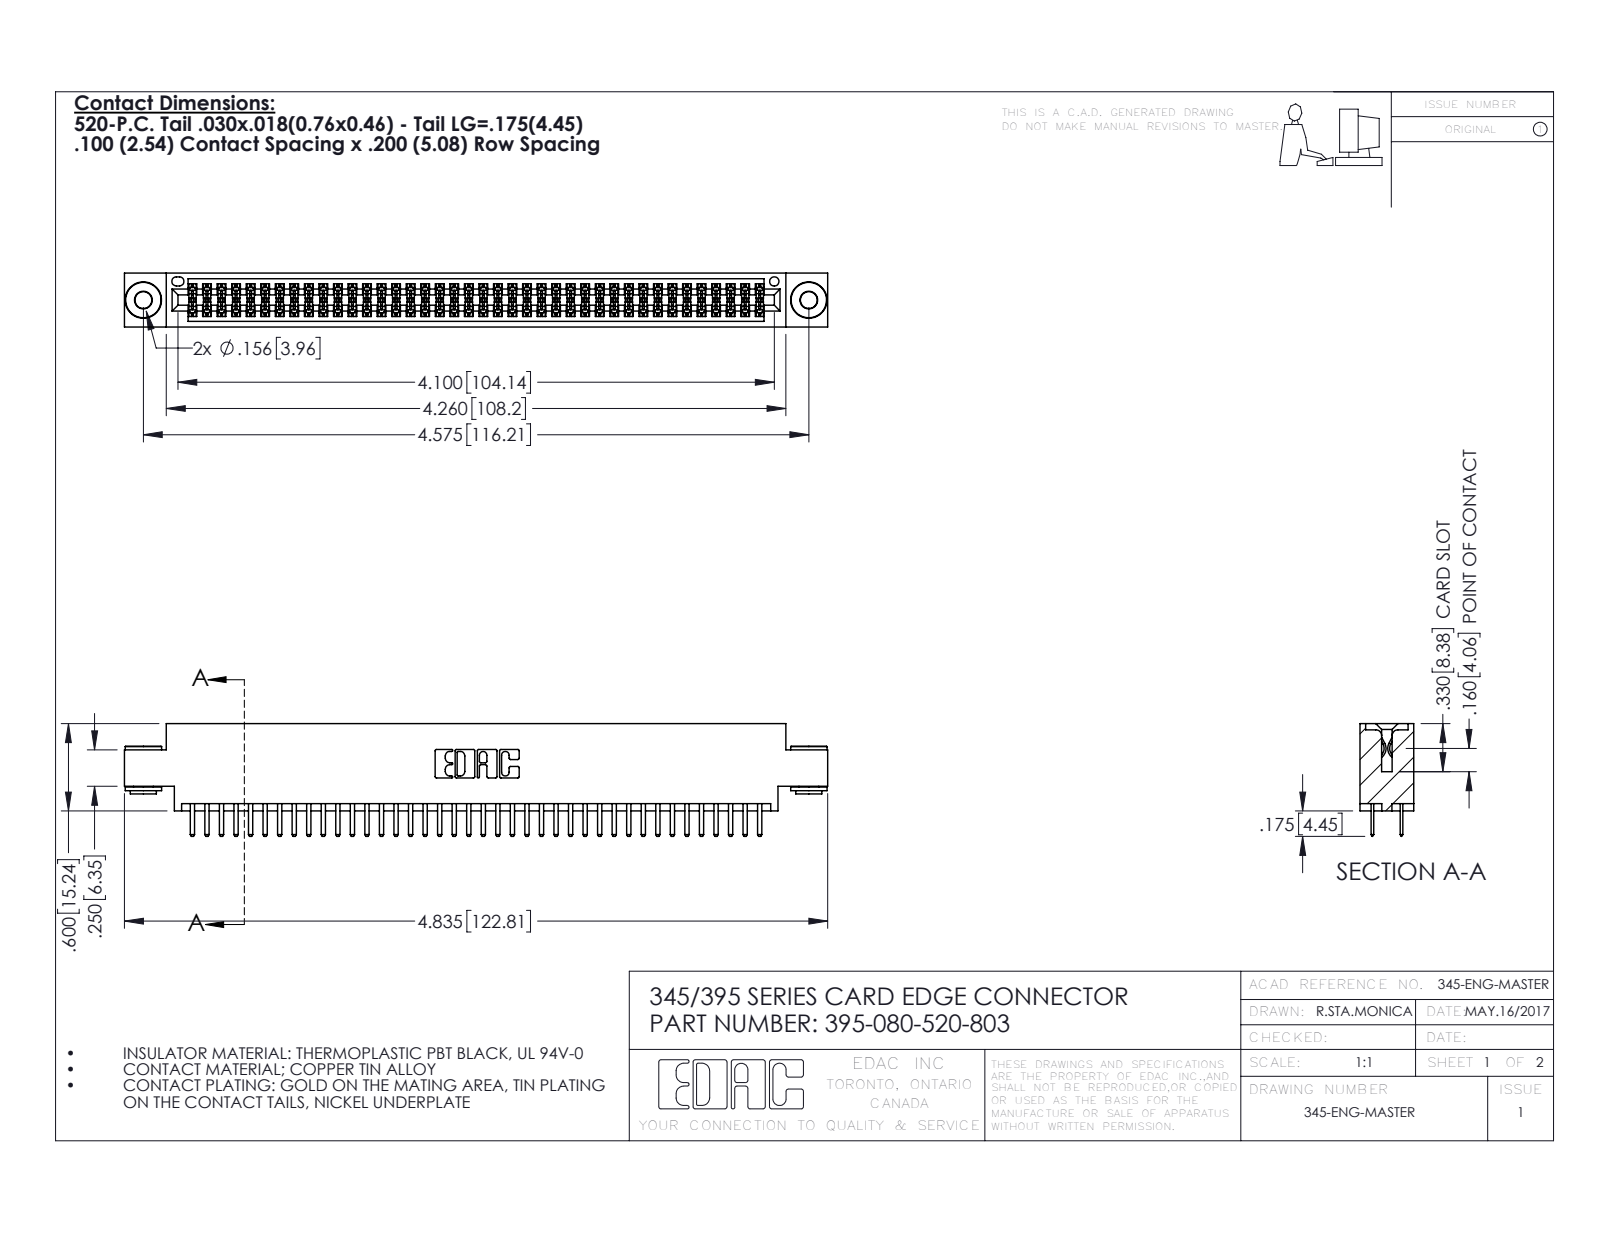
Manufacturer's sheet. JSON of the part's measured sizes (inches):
{"part_name": "345 Part_0.170 Offset - 0.156 Dia-TH; 345-250-002_345-250-002-102; 345-292-001_345-293-120; 395-080-520-803", "step_written_by": "SolidWorks 2016 (CONFIG_CONTROL_DESIGN)", "units": "inches", "bodies": {"solids": 83, "faces": 4488, "planar": 2894, "cylindrical": 1586, "other": 8}, "overall_size": [4.835, 0.775, 0.37], "volume_in3": 0.719, "surface_area_in2": 27.36, "round_holes": [[0.116, 2], [0.156, 2], [0.064, 1]], "round_bosses_or_shafts": [[0.25, 2], [0.18, 2], [0.136, 2]], "partial_cylinders_radius": [[0.006, 120], [0.01, 84], [0.01, 22], [0.007, 6], [0.031, 6], [0.026, 3], [0.014, 2], [0.019, 2]], "face_to_face_distances": [0.072, 0.298, 0.2, 0.37, 0.098, 0.272, 0.025, 0.225, 0.175, 0.022], "hole_center_spacings": [0.27, 4.339, 4.575]}
